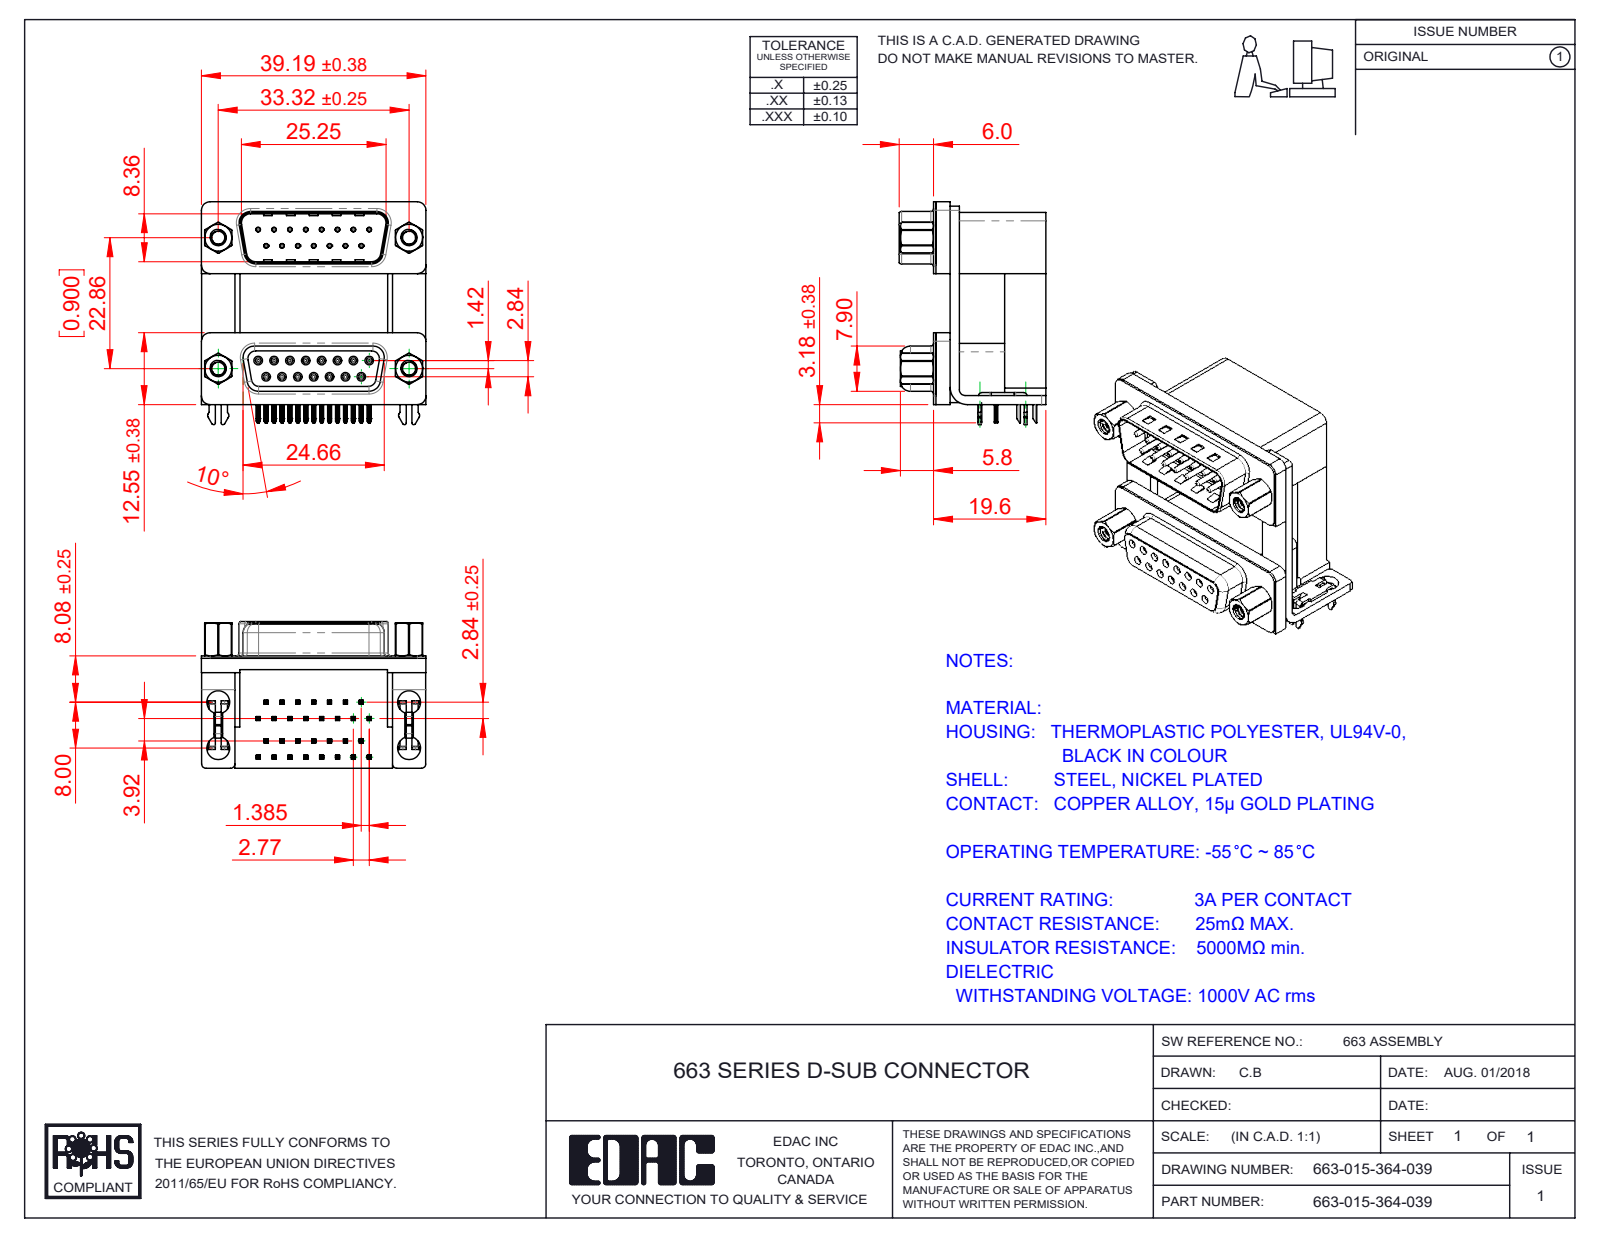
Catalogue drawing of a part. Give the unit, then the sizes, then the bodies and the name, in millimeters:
Units: millimetres
Overall size (bounding box): 39.19 × 38.91 × 25.6
Round holes (diameter × count): ⌀0.8 ×30, ⌀0.35 ×15, ⌀0.9 ×15, ⌀4 ×8, ⌀2.26 ×4, ⌀2.29 ×4, ⌀3.5 ×4, ⌀4.8 ×4, ⌀5 ×4
Round bosses / shafts (diameter × count): ⌀1.2 ×15, ⌀0.75 ×15, ⌀4.9 ×4, ⌀4.75 ×4, ⌀3.9 ×4, ⌀2.79 ×4
Partial cylindrical surfaces — rounded edges, fillets, slot ends (radius × count): R0.1 ×122, R0.25 ×70, R0.15 ×60, R0.12 ×30, R0.35 ×30, R0.5 ×16, R1.5 ×16, R0.34 ×15
Main face-to-face distances: 0.4, 19.2, 12, 7.2, 16.7, 9.5, 2.5, 12.4, 10.7, 1.6
Hole centre spacings: 3.16, 23.03, 2.77, 23.52, 5.54, 8.31, 22.86, 24.32
Volume: 16 431 mm³ · Surface area: 18 665 mm²
Bodies: 47 solids, 4316 faces (2161 planar, 1208 cylindrical, 947 other)
Part name (STEP PRODUCT): 663 Contact Top Lower; 663 Contact Bottom Upper_H; 663 Housing Upper_15 Contacts H; 663 Contact Top Upper_H (+8 more)
STEP written by: SolidWorks 2020 (CONFIG_CONTROL_DESIGN)
